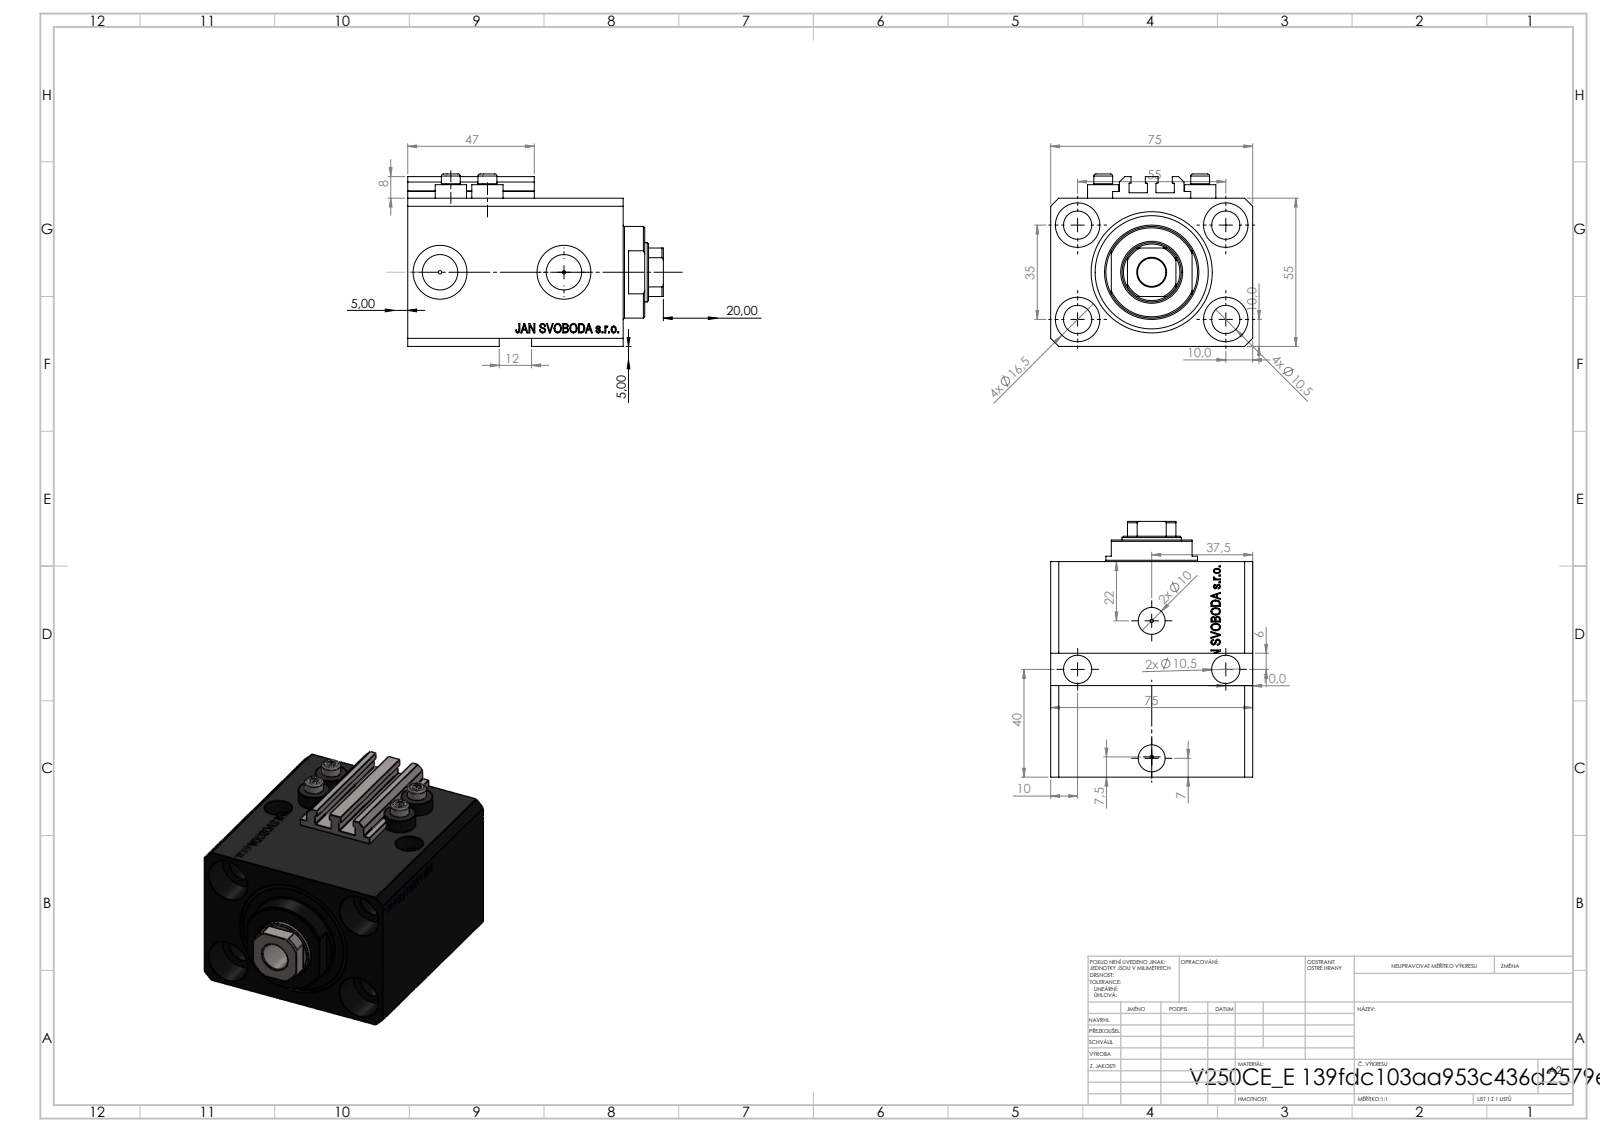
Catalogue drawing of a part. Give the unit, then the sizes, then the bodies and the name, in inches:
Units: inches
Overall size (bounding box): 3.74 × 2.953 × 2.52
Round holes (diameter × count): ⌀0.413 ×7, ⌀0.049 ×4, ⌀0.157 ×4, ⌀0.65 ×4, ⌀0.394 ×2, ⌀0.518 ×2, ⌀0.787 ×2, ⌀0.866 ×1, ⌀1.26 ×1, ⌀1.772 ×1
Round bosses / shafts (diameter × count): ⌀0.457 ×4, ⌀0.276 ×4, ⌀1.339 ×1
Partial cylindrical surfaces — rounded edges, fillets, slot ends (radius × count): R0.008 ×10, R0.413 ×1
Main face-to-face distances: 2.165, 2.953, 0.591, 3.15, 2.559, 0.118, 2.169, 0.39, 2.76, 2.126
Hole centre spacings: 1.283, 2.165, 0.535, 0.555, 0.783, 0.792, 1.016, 1.121
Volume: 17.32 in³ · Surface area: 115.4 in²
Bodies: 8 solids, 1064 faces (514 planar, 126 cylindrical, 424 other)
Part name (STEP PRODUCT): V250CE_C_VCP; ALLEN BOLT V250CE; V250CE_VC_E; V250CE_E_Body
STEP written by: SolidWorks 2019 (CONFIG_CONTROL_DESIGN)
